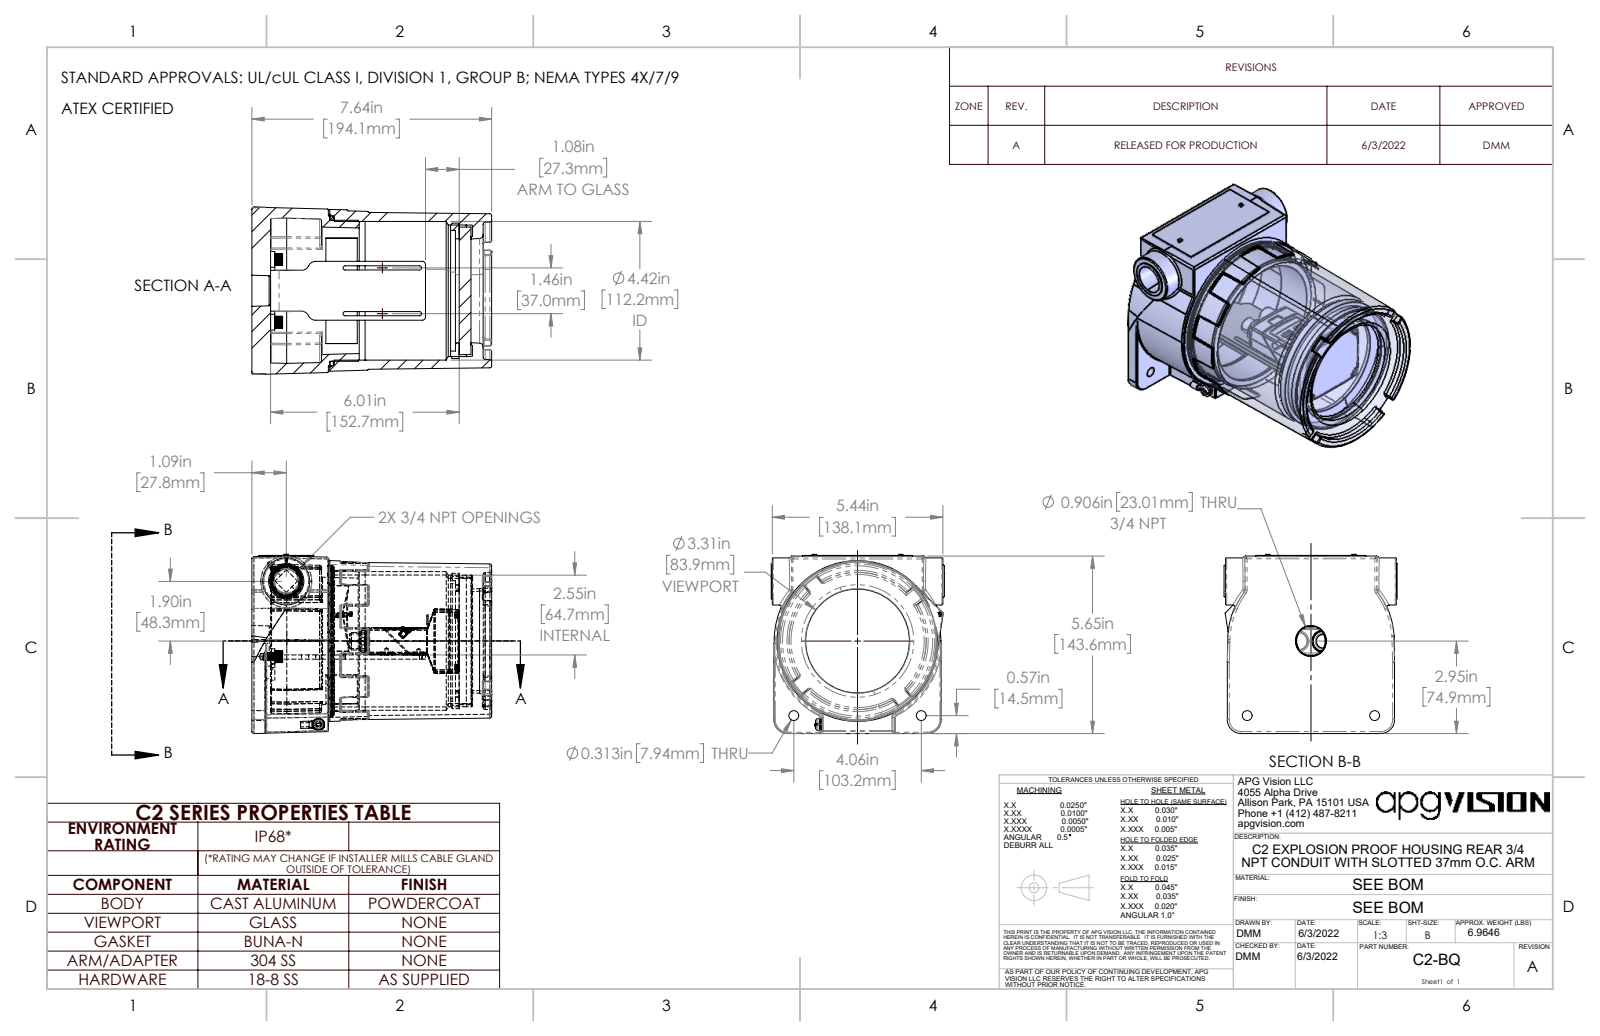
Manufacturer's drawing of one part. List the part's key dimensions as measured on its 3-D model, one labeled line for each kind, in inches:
Part name (STEP PRODUCT): 91292A111_91292A111; 201109; C2-BQ; IS2000_3D_straight (+2 more)
STEP written by: SolidWorks 2021 (CONFIG_CONTROL_DESIGN)
Units: inches
Bodies: 25 solids, 3614 faces (913 planar, 856 cylindrical, 1845 other)
Overall size (bounding box): 7.643 × 5.71 × 5.519
Volume: 73.25 in³ · Surface area: 493.4 in²
Round holes (diameter × count): ⌀0.098 ×4, ⌀0.177 ×4, ⌀0.067 ×2, ⌀0.094 ×2, ⌀0.145 ×2, ⌀0.188 ×2, ⌀0.201 ×2, ⌀0.313 ×2, ⌀0.4 ×2, ⌀0.107 ×1, ⌀0.129 ×1, ⌀0.195 ×1
Round bosses / shafts (diameter × count): ⌀0.217 ×4, ⌀0.15 ×4, ⌀0.118 ×4, ⌀0.093 ×4, ⌀0.25 ×2, ⌀0.19 ×2, ⌀0.185 ×2, ⌀0.157 ×2
Partial cylindrical surfaces — rounded edges, fillets, slot ends (radius × count): R0.008 ×46, R0.039 ×28, R0.006 ×20, R0.01 ×20, R0.031 ×19, R0.03 ×18, R0.031 ×11, R0.02 ×10
Main face-to-face distances: 0.594, 6.982, 6.388, 6.607, 6.013, 0.375, 0.135, 0.02, 3.307, 3.172
Hole centre spacings: 1.118, 0.335, 0.707, 1.02, 1.319, 1.457, 1.54, 1.581
